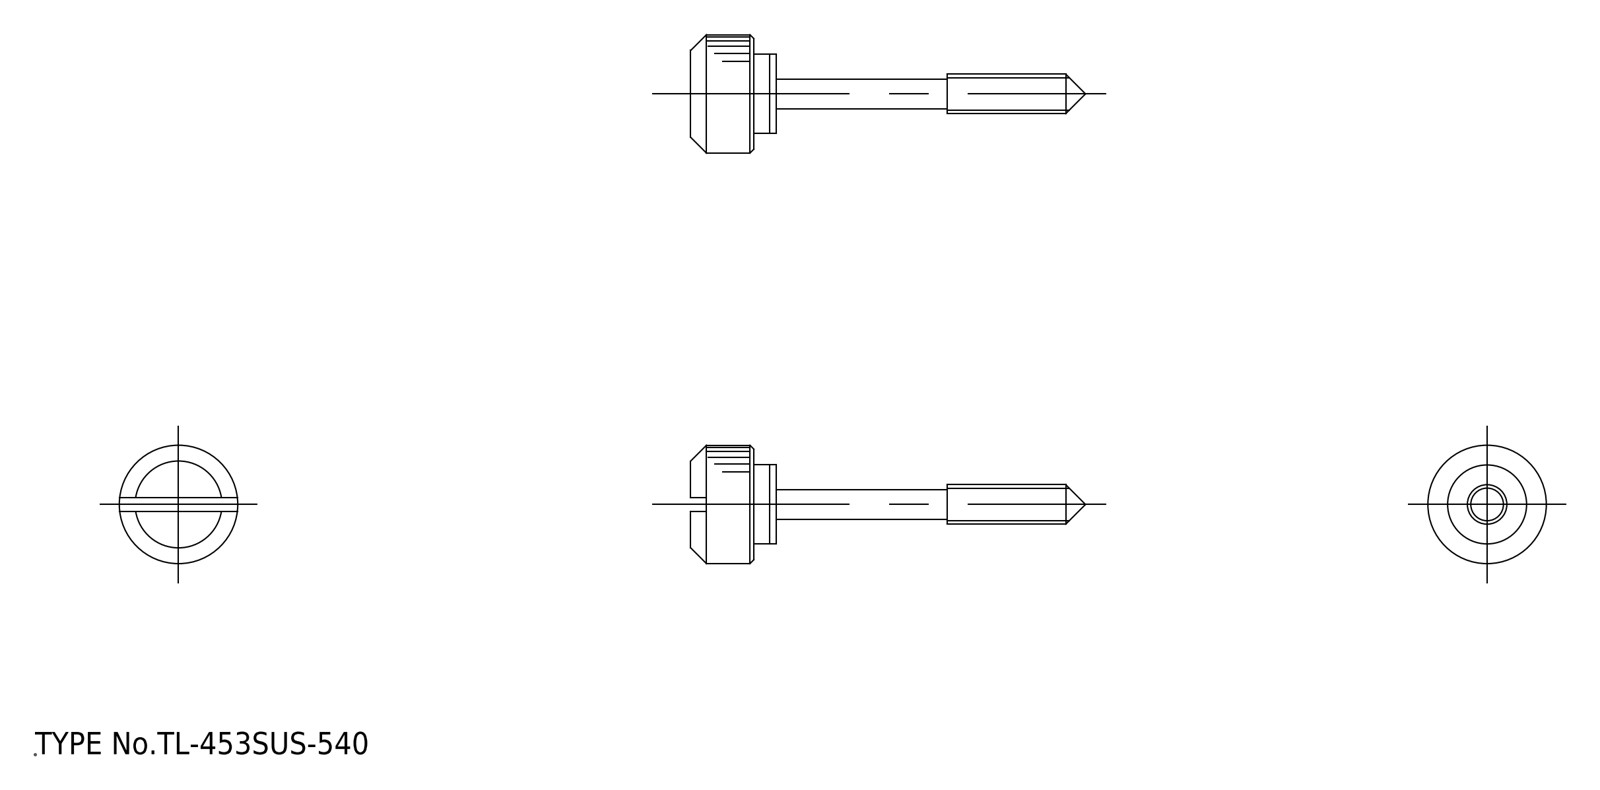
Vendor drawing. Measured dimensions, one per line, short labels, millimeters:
name: washer; knob
written by: spGate 19.8.4 (****-****-****-****) (AUTOMOTIVE_DESIGN)
unit: mm
bodies: 2 solids, 42 faces (18 planar, 18 cylindrical, 6 other)
size: 50 × 15 × 15
volume: 2 047 mm³; area: 1 458 mm²
bosses: 1× ⌀15, 1× ⌀10, 1× ⌀5, 1× ⌀3.8
rounds: 4× R0.8, 1× R1.95
face distances: 2, 8, 10, 10.8, 2.8, 0.8, 6, 8.8, 1.8, 32.5
